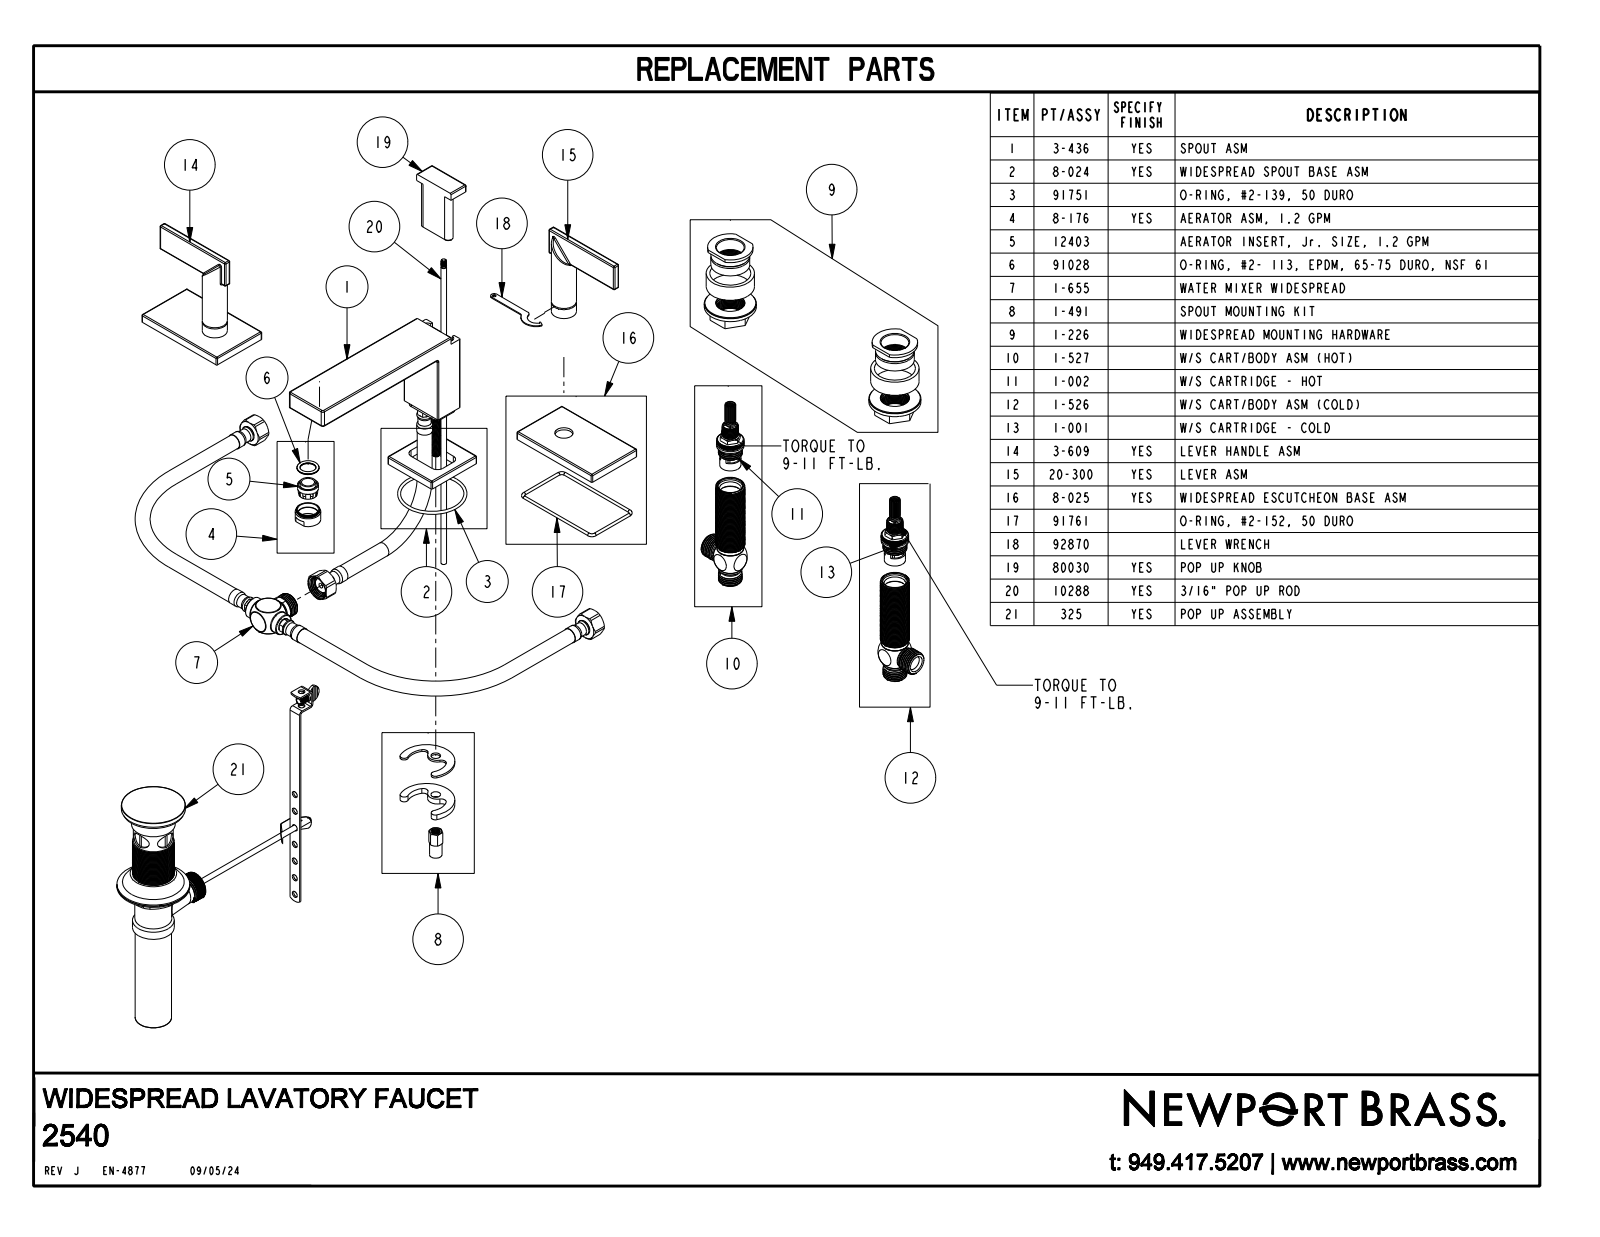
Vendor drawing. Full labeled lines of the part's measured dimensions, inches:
Part name (STEP PRODUCT): 2540
STEP written by: CREO PARAMETRIC BY PTC INC, 2018400 (CONFIG_CONTROL_DESIGN)
Units: inches
Bodies: 3 solids, 214 faces (58 planar, 92 cylindrical, 64 other)
Overall size (bounding box): 13.12 × 7.247 × 3.51
Volume: 22.94 in³ · Surface area: 125.1 in²
Round bosses / shafts (diameter × count): ⌀0.86 ×2, ⌀0.68 ×2, ⌀0.875 ×1
Partial cylindrical surfaces — rounded edges, fillets, slot ends (radius × count): R0.04 ×61, R0.08 ×3
Main face-to-face distances: 0.31, 3.46, 3.15, 0.425, 0.661, 2.806, 2.496, 0.654, 1.67, 0.557
